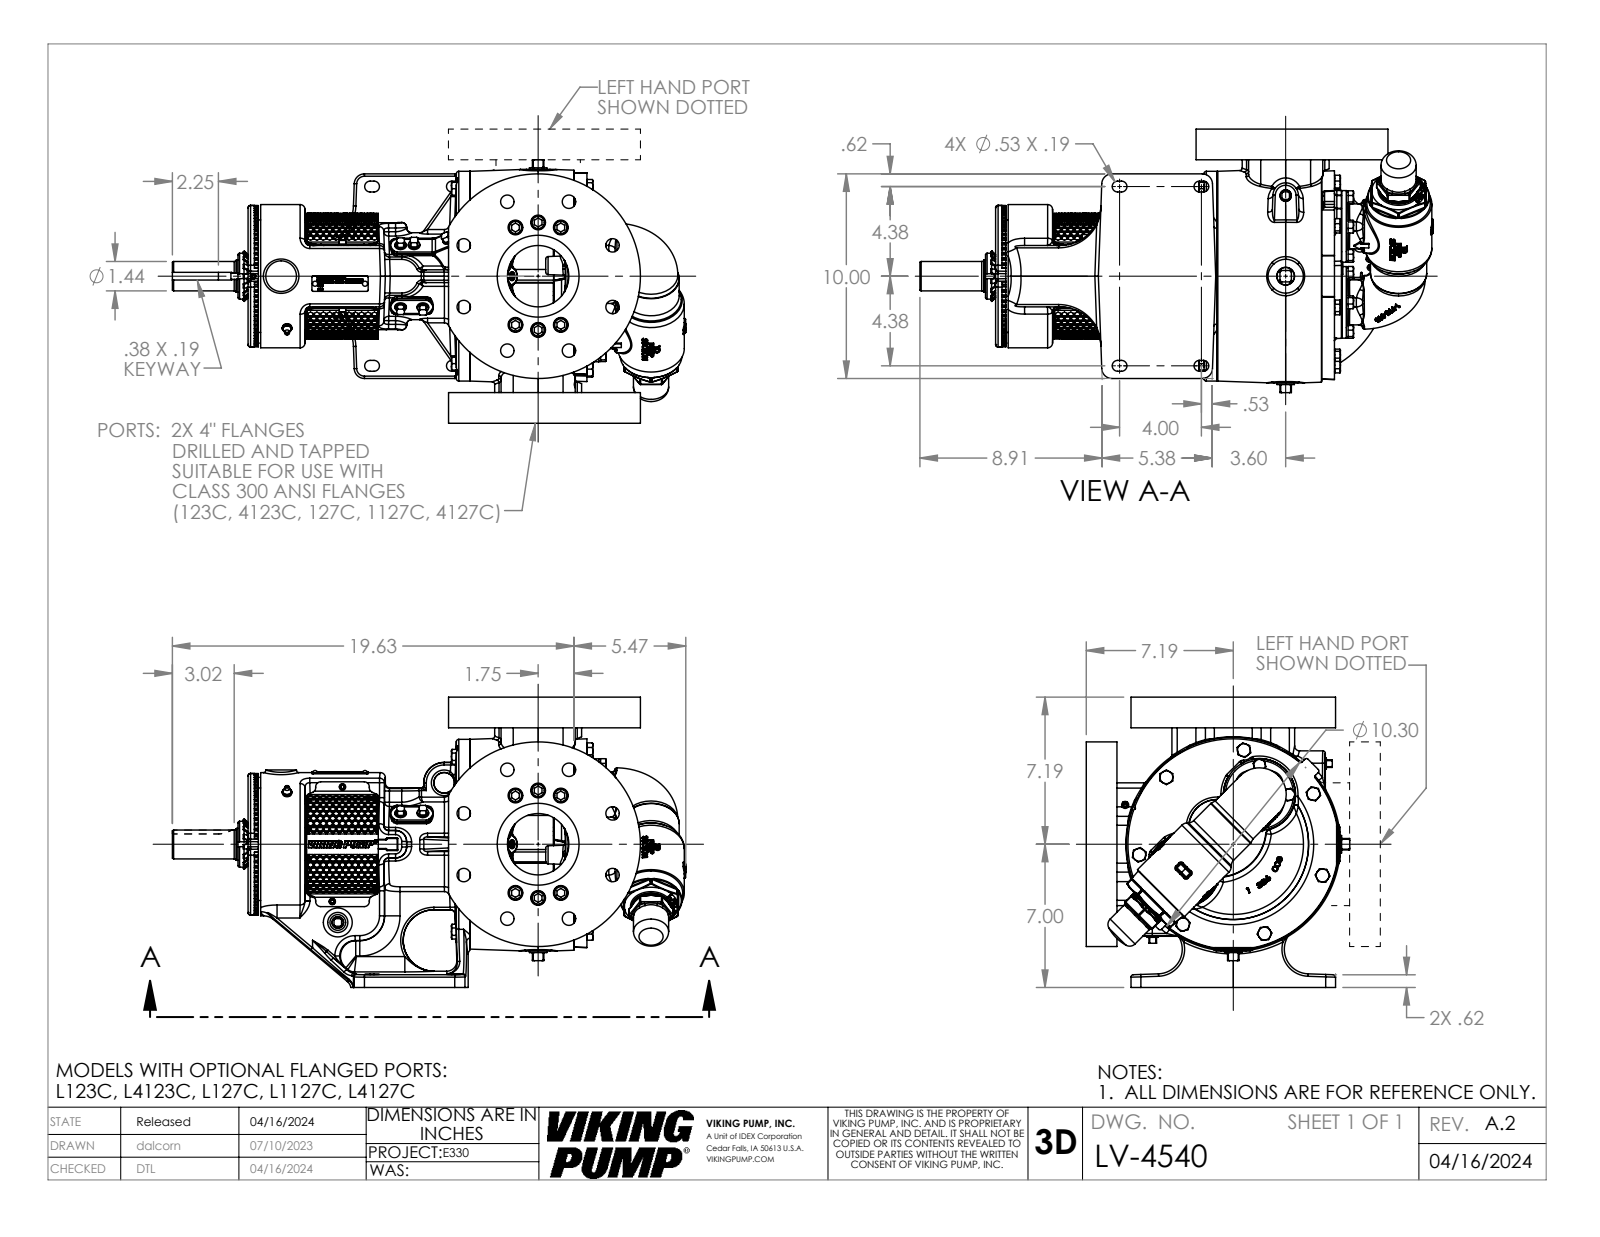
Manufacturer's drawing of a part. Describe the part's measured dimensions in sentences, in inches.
The part is named "LV-4540". Its 3-D file was written by "SolidWorks 2022 (AUTOMOTIVE_DESIGN)". It is 1 solid with 5404 faces: 1774 planar, 1078 cylindrical and 2552 other. Overall it measures 25.099 by 14.188 by 12.878 inches. Its volume is 1 110 cubic inches and its surface area 1 660 square inches. Round holes: 16 of diameter 0.656, 12 of diameter 0.469, 12 of diameter 0.719, 8 of diameter 1.094, 6 of diameter 0.199, 6 of diameter 0.25, 3 of diameter 0.159, 2 of diameter 0.266, 2 of diameter 0.313, 2 of diameter 3, 1 of diameter 0.453, 1 of diameter 1.552. Round bosses or shafts: 15 of diameter 0.437, 12 of diameter 0.66, 12 of diameter 0.625, 3 of diameter 3.5, 3 of diameter 0.625, 3 of diameter 0.312, 2 of diameter 10, 1 of diameter 10.25. Partial cylindrical surfaces (rounded edges, fillets, slot ends): 109 of radius 0.063, 76 of radius 0.12, 74 of radius 0.069, 48 of radius 0.24, 26 of radius 0.06, 24 of radius 0.03, 16 of radius 1, 12 of radius 0.25. The main face-to-face distances are 1.5, 12.687, 14.187, 0.5, 16.066, 13.816, 2.25, 3.546, 10.27, 2.134. The hole center spacings are 7.276, 3, 3.937, 2.625, 1.375, 1.136, 2.18, 2.675.
